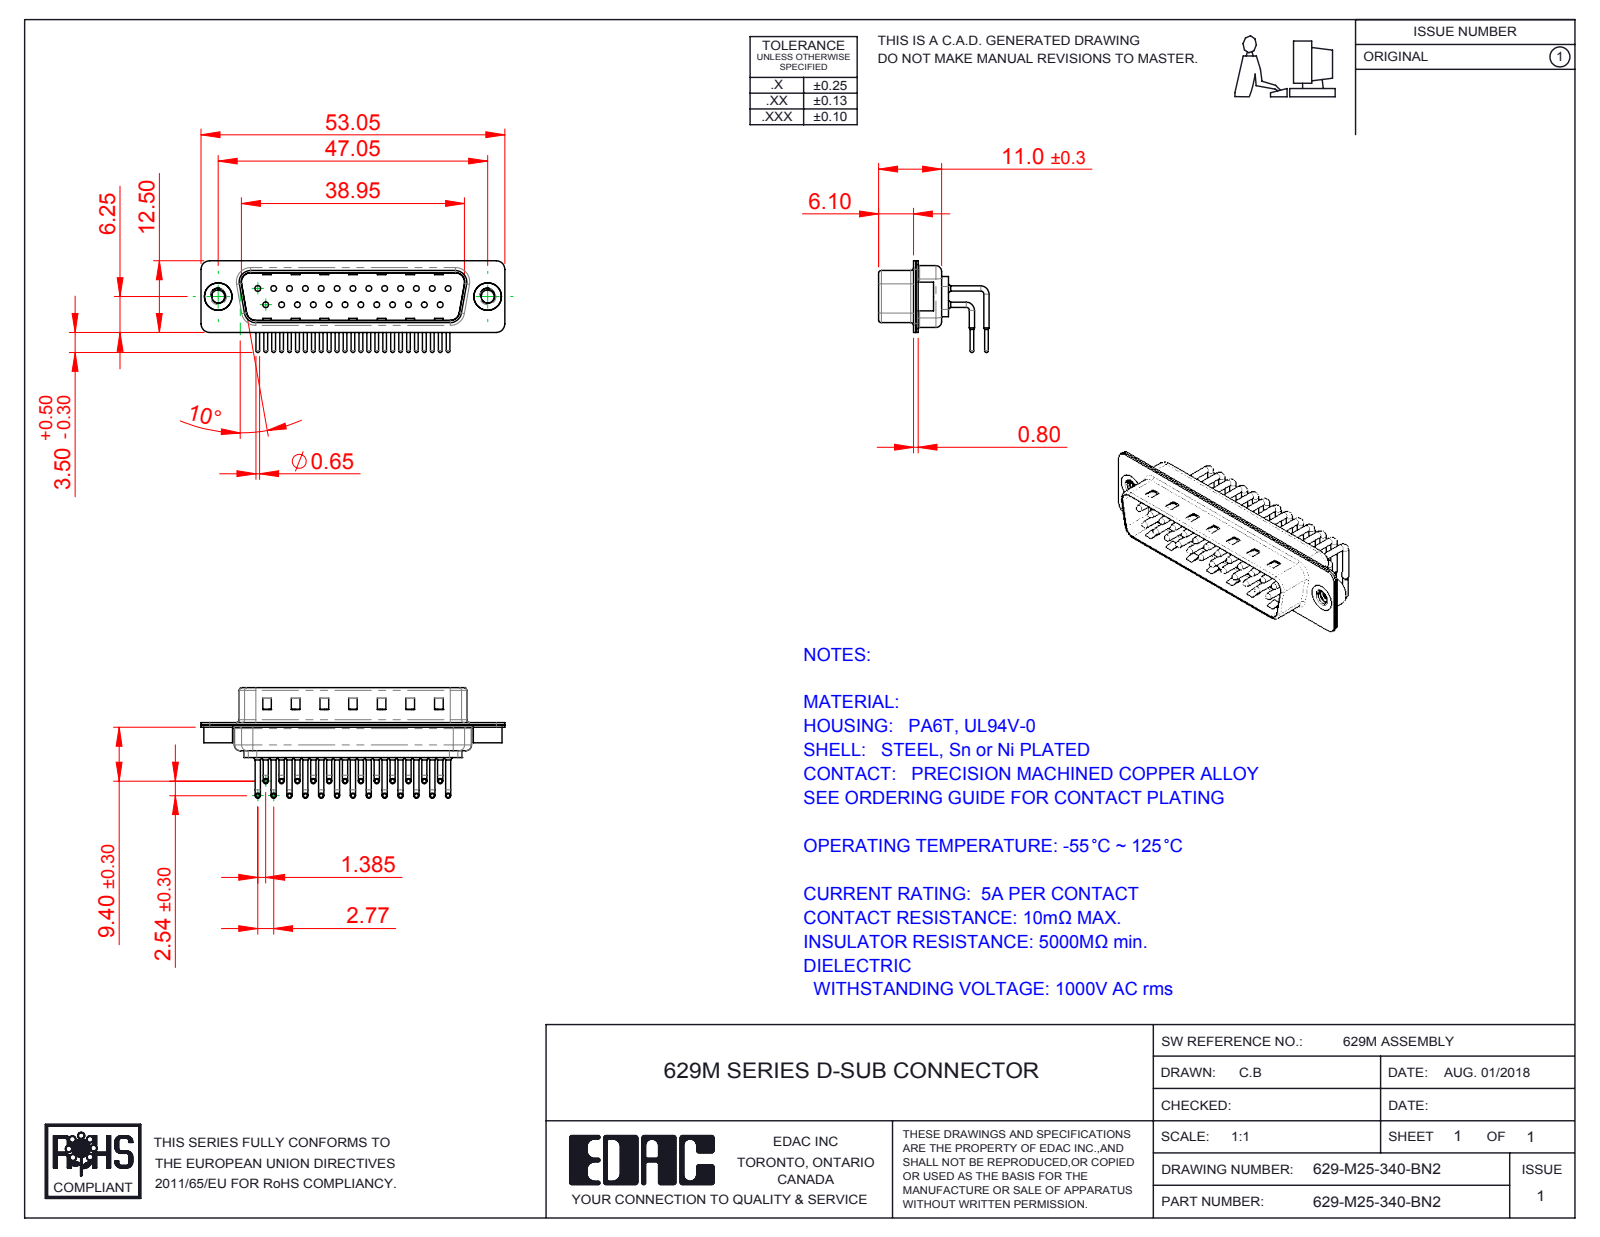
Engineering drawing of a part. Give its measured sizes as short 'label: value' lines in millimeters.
name: 629M Contact Row 1; 629M Shell Front_25 Contacts; 629M Contact Row 2; 629-M25-340-BN2 (+3 more)
written by: SolidWorks 2016 (CONFIG_CONTROL_DESIGN)
unit: mm
bodies: 30 solids, 3126 faces (1771 planar, 1037 cylindrical, 318 other)
size: 53.05 × 19.29 × 16
volume: 2 911 mm³; area: 7 760 mm²
holes: 25× ⌀1, 25× ⌀1.7, 25× ⌀2, 2× ⌀2.26, 2× ⌀4, 2× ⌀4.8
bosses: 50× ⌀0.9, 25× ⌀1.5, 25× ⌀0.65, 2× ⌀5, 2× ⌀4.9
rounds: 25× R1.01, 16× R1.5, 12× R2, 8× R0.5, 8× R1.6, 4× R0.25, 4× R0.6, 4× R0.65
face distances: 0.4, 0.85, 9.55, 8.7, 1.25, 10.4, 1.5, 1.9, 0.35, 6.1
hole spacings: 3.16, 2.77, 5.54, 8.31, 11.08, 13.85, 5.04, 7.49
